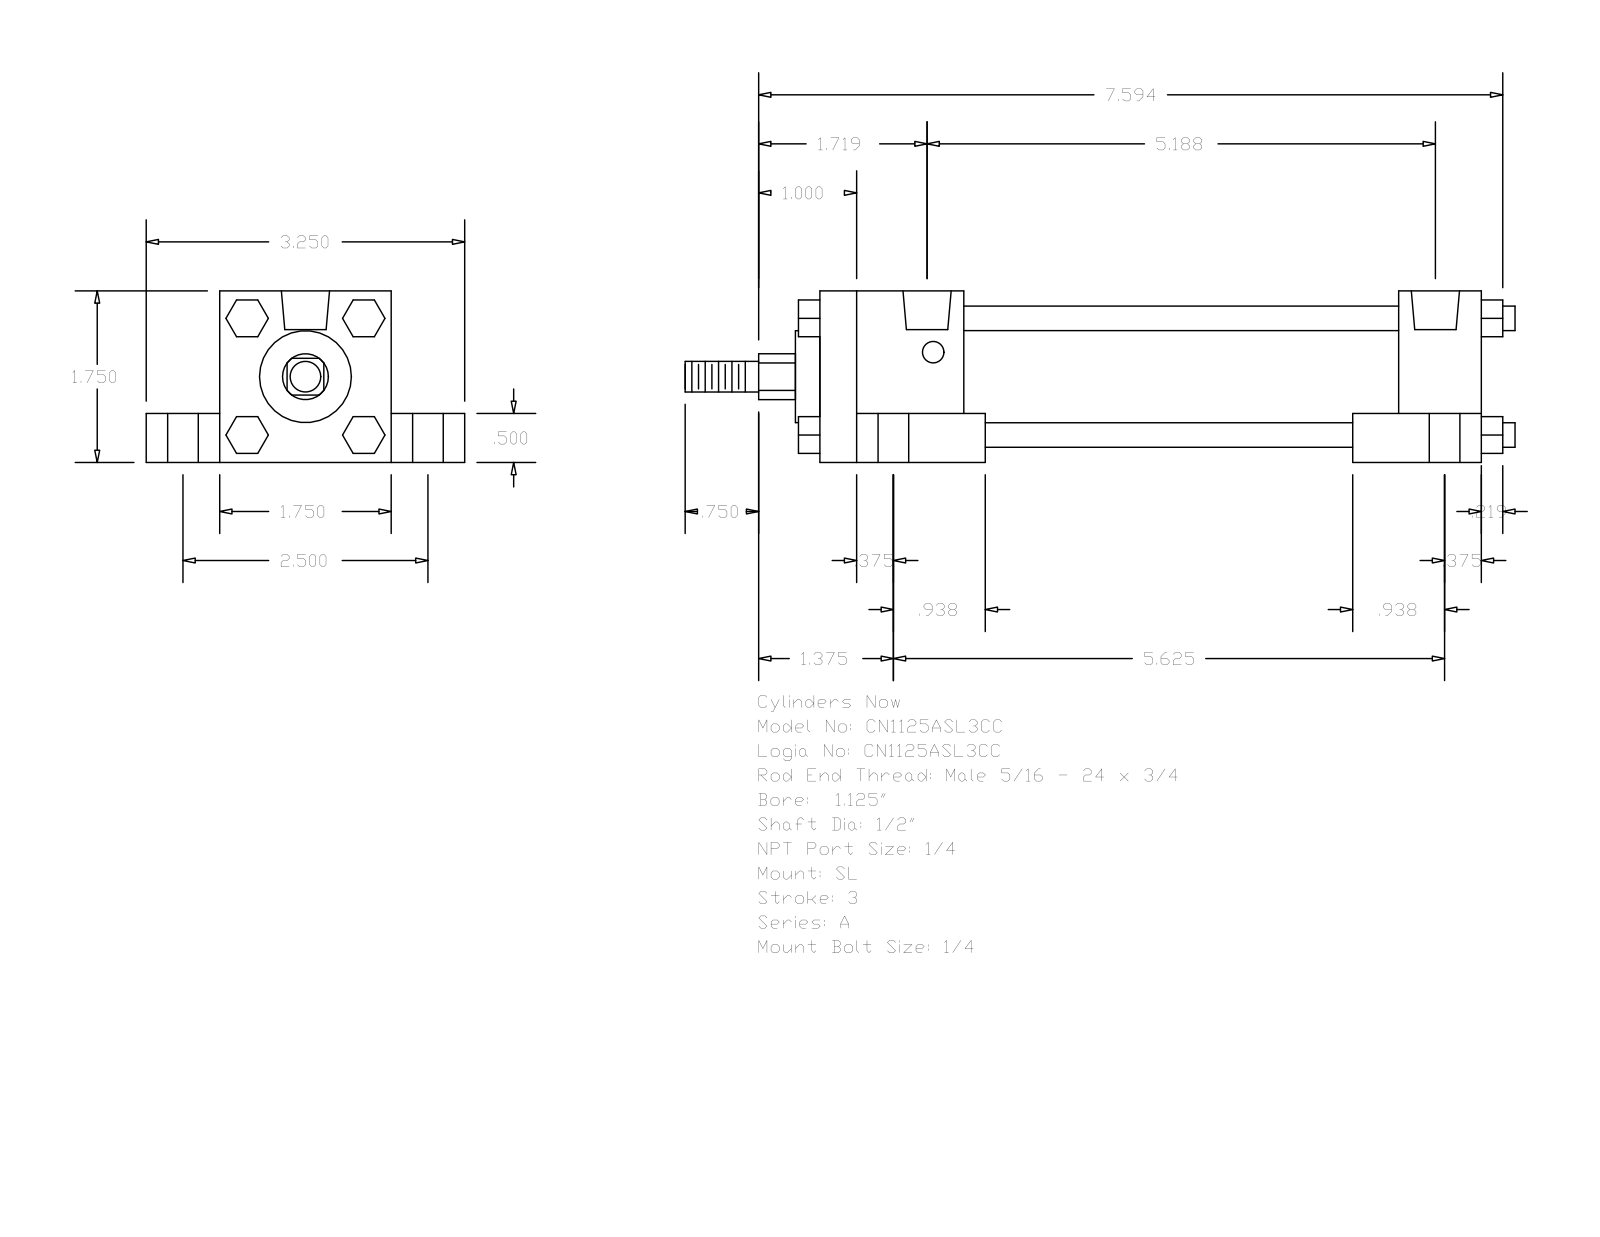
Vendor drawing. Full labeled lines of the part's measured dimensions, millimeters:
Part name (STEP PRODUCT): A_SL__0112_0.5
STEP written by: GSSL Pune (CONFIG_CONTROL_DESIGN)
Units: millimetres
Bodies: 0 solids, 150 faces (114 planar, 36 cylindrical, 0 other)
Overall size (bounding box): 215.11 × 82.55 × 44.45
Round holes (diameter × count): ⌀5.56 ×4, ⌀7.94 ×4, ⌀14.29 ×4, ⌀12.49 ×2
Round bosses / shafts (diameter × count): ⌀6.35 ×4, ⌀31.88 ×1, ⌀23.81 ×1, ⌀12.7 ×1, ⌀7.94 ×1
Partial cylindrical surfaces — rounded edges, fillets, slot ends (radius × count): R5.94 ×1
Main face-to-face distances: 44.46, 31.76, 12.7, 19.04, 63.5, 134.14, 171.44, 150.01, 21.43, 37.3
Hole centre spacings: 31.84, 32, 32.93, 33.39, 63.5, 128.59, 136.31, 137.85
